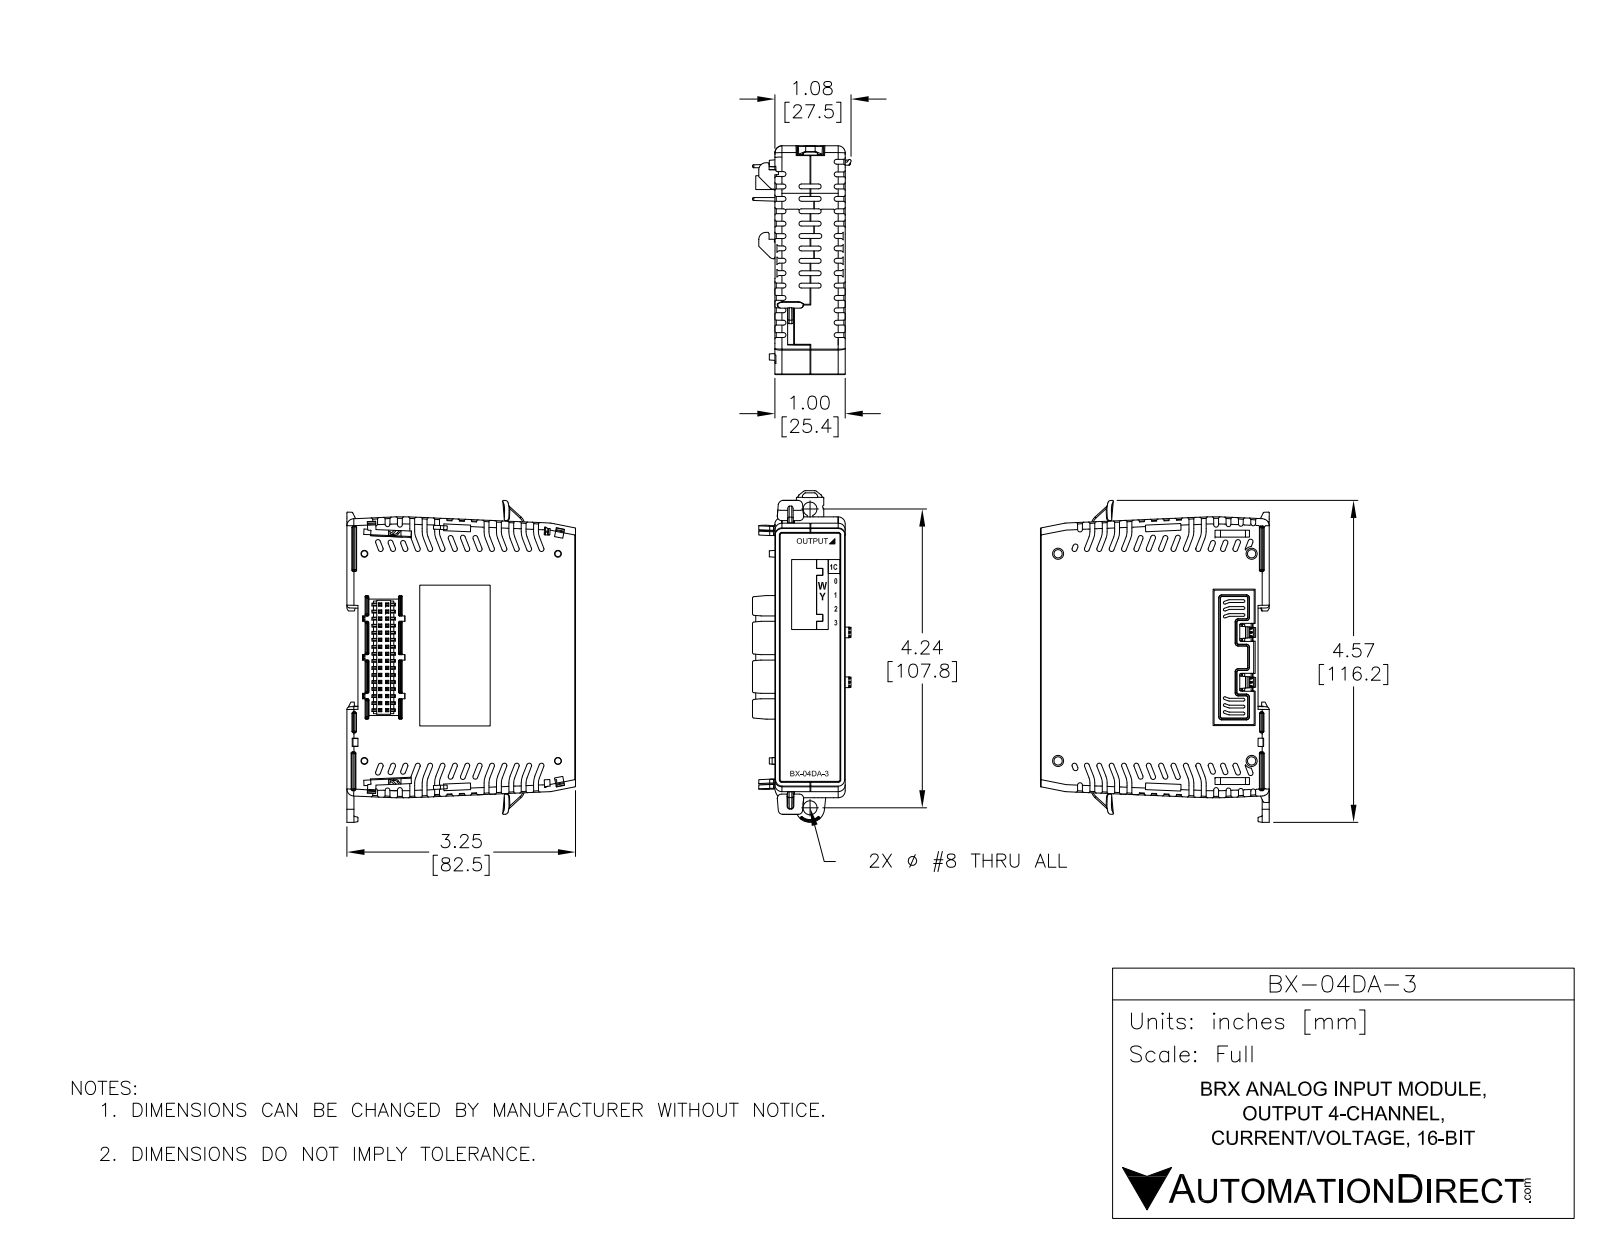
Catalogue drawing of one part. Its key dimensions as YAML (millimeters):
part_name: "BX-04DA-3"
step_written_by: "SolidWorks 2017 (AUTOMOTIVE_DESIGN)"
units: millimeters
bodies: {solids: 4, faces: 3486, planar: 2476, cylindrical: 573, other: 437}
overall_size: [116.5, 82.6, 35.6]
volume: 189800
surface_area: 46760
round_holes:
  - {diameter: 1.2, count: 2}
  - {diameter: 1.7, count: 2}
  - {diameter: 3, count: 2}
  - {diameter: 3, count: 2}
  - {diameter: 5.1, count: 1}
round_bosses_or_shafts:
  - {diameter: 1.6, count: 2}
  - {diameter: 1.5, count: 2}
partial_cylinders:
  - {radius: 0.1, count: 102}
  - {radius: 0.3, count: 47}
  - {radius: 0.2, count: 41}
  - {radius: 0.5, count: 34}
  - {radius: 0.1, count: 24}
  - {radius: 3, count: 14}
  - {radius: 1, count: 13}
  - {radius: 0.3, count: 12}
face_to_face_distances: [25.4, 81.6, 81.8, 12.1, 4, 77.5, 77.8, 2.5, 1, 20]
hole_center_spacings: [2.5, 20.9, 23.3, 33, 53.2, 55.7, 65.7, 66.5]
